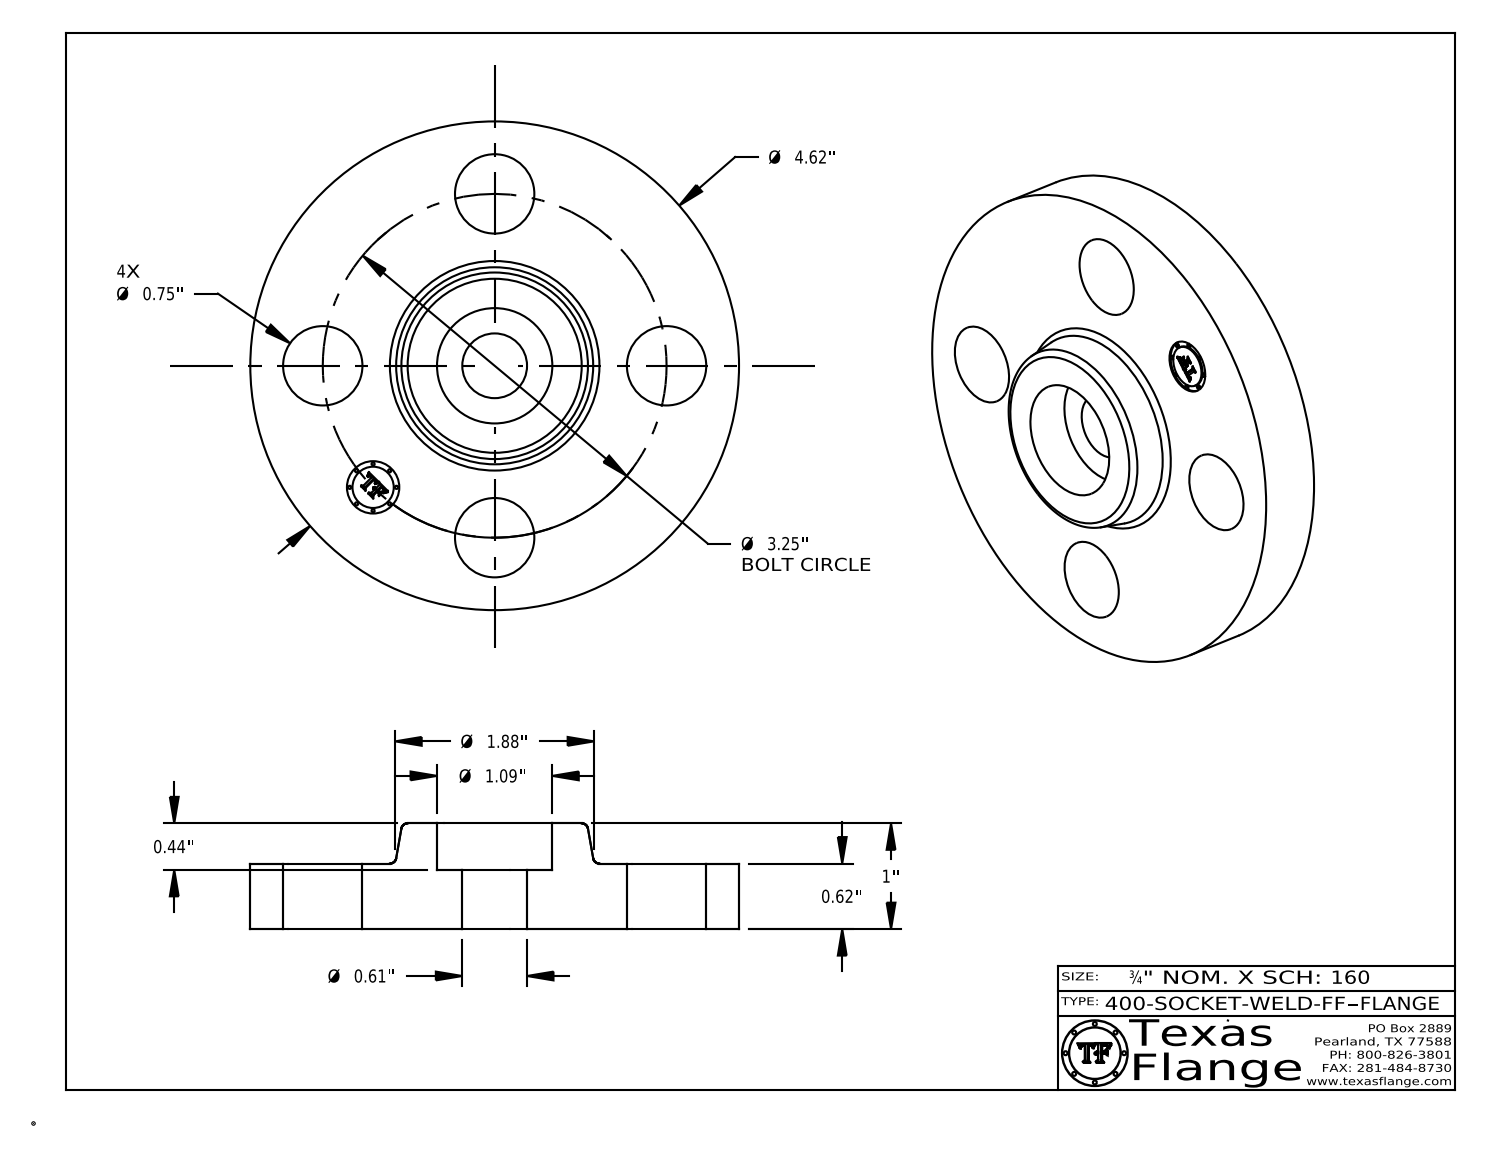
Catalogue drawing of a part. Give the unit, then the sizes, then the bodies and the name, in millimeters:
Units: millimetres
Overall size (bounding box): 117.3 × 117.3 × 25.4
Round holes (diameter × count): ⌀19.1 ×4, ⌀12.6 ×1, ⌀15.5 ×1, ⌀27.7 ×1
Round bosses / shafts (diameter × count): ⌀0.8 ×8, ⌀117.3 ×1, ⌀9.9 ×1
Main face-to-face distances: 15.7, 25.4, 9.7, 14.2, 1.5, 11.2, 15.4, 1.1, 0.4, 10
Hole centre spacings: 41.3, 58.4, 31.6, 76.3, 82.6
Volume: 159 000 mm³ · Surface area: 31 320 mm²
Bodies: 1 solid, 409 faces (369 planar, 34 cylindrical, 6 other)
Part name (STEP PRODUCT): 400-SOCKET-WELD-FF
STEP written by: CATIA V5 STEP AP214 (AUTOMOTIVE_DESIGN)
